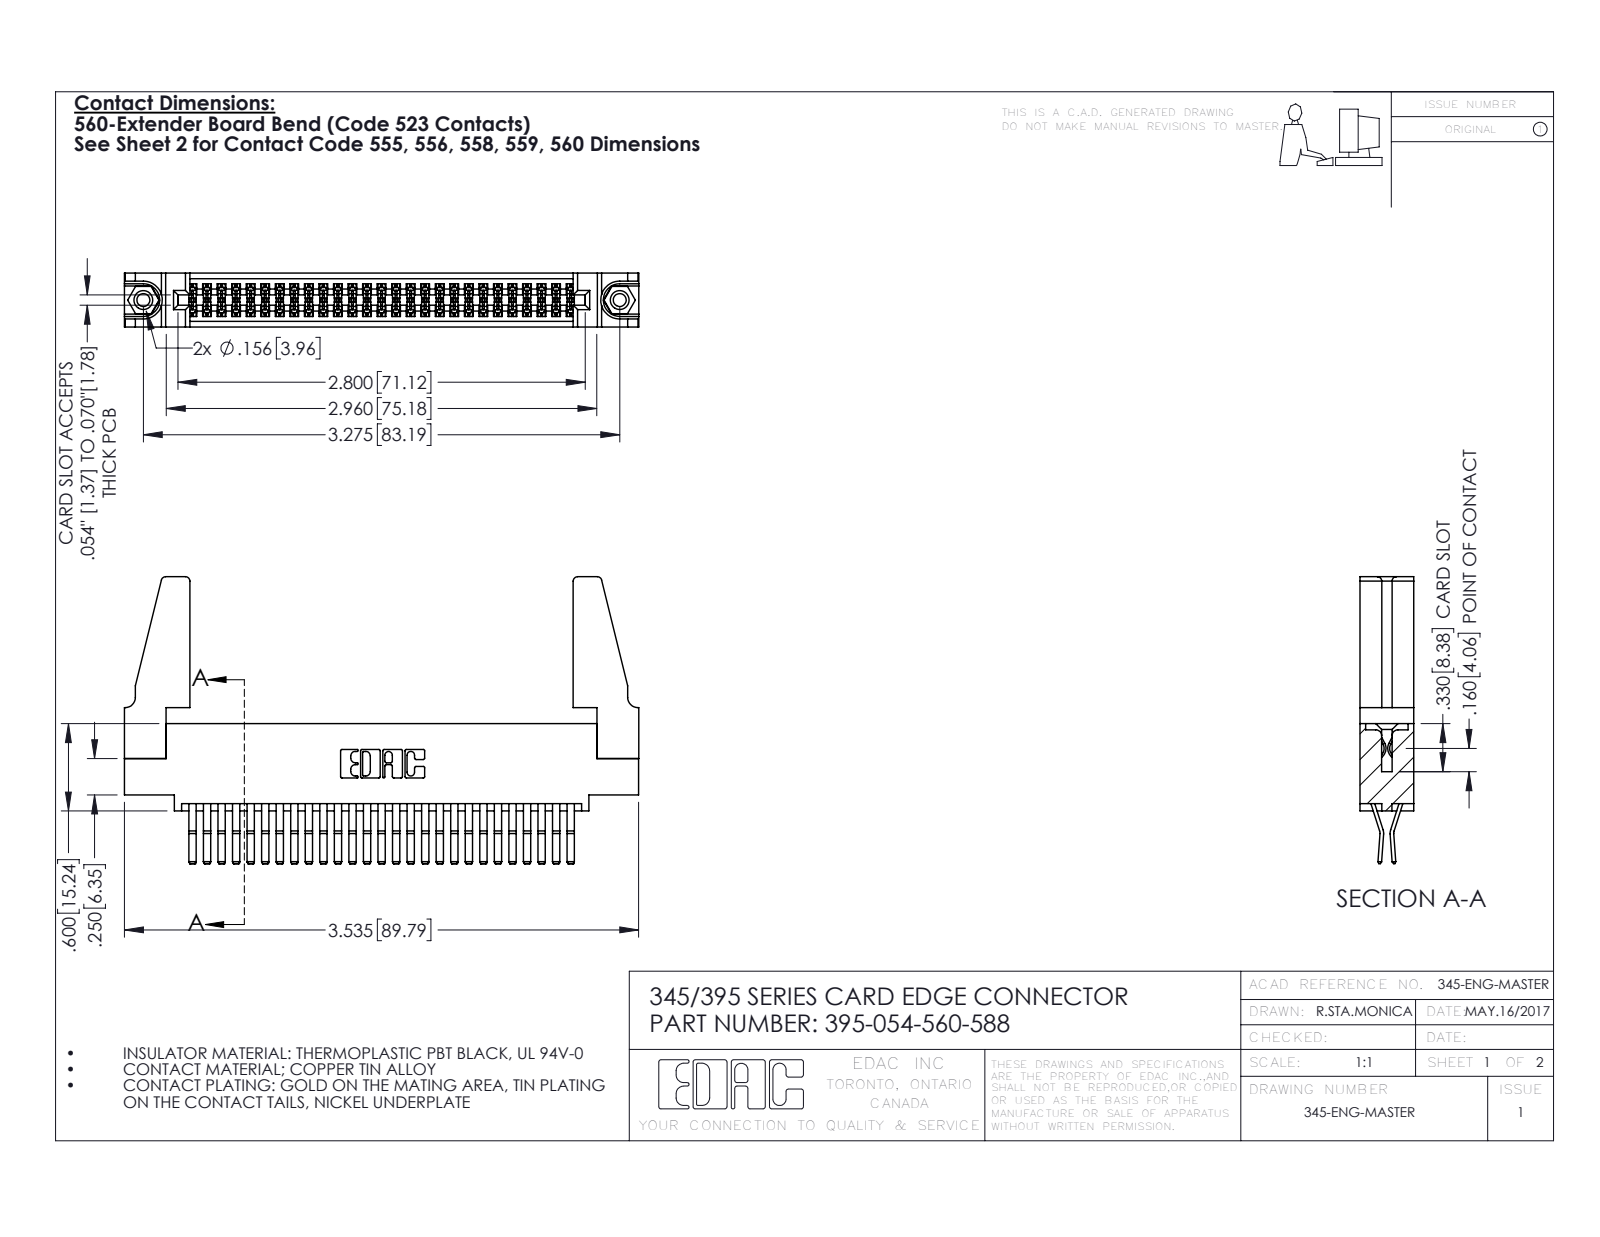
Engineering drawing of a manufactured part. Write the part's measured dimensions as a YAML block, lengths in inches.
part_name: "345-220-078_345-220-088; 395-054-560-588; 345 Part_0.110 Offset - 0.156 Dia-TH; 345-250-001_345-250-001-102 (+1 more)"
step_written_by: "SolidWorks 2016 (CONFIG_CONTROL_DESIGN)"
units: inches
bodies: {solids: 59, faces: 3062, planar: 1938, cylindrical: 1108, other: 16}
overall_size: [3.536, 1.972, 0.37]
volume: 0.74
surface_area: 26.26
round_holes:
  - {diameter: 0.089, count: 2}
  - {diameter: 0.125, count: 2}
  - {diameter: 0.156, count: 2}
  - {diameter: 0.064, count: 1}
round_bosses_or_shafts:
  - {diameter: 0.155, count: 2}
partial_cylinders:
  - {radius: 0.006, count: 81}
  - {radius: 0.01, count: 22}
  - {radius: 0.03, count: 8}
  - {radius: 0.007, count: 6}
  - {radius: 0.031, count: 6}
  - {radius: 0.026, count: 3}
  - {radius: 0.01, count: 2}
  - {radius: 0.014, count: 2}
face_to_face_distances: [0.072, 0.298, 0.37, 0.025, 0.2, 0.098, 0.272, 0.225, 0.175, 0.149]
hole_center_spacings: [0.27, 3.04, 3.275]
